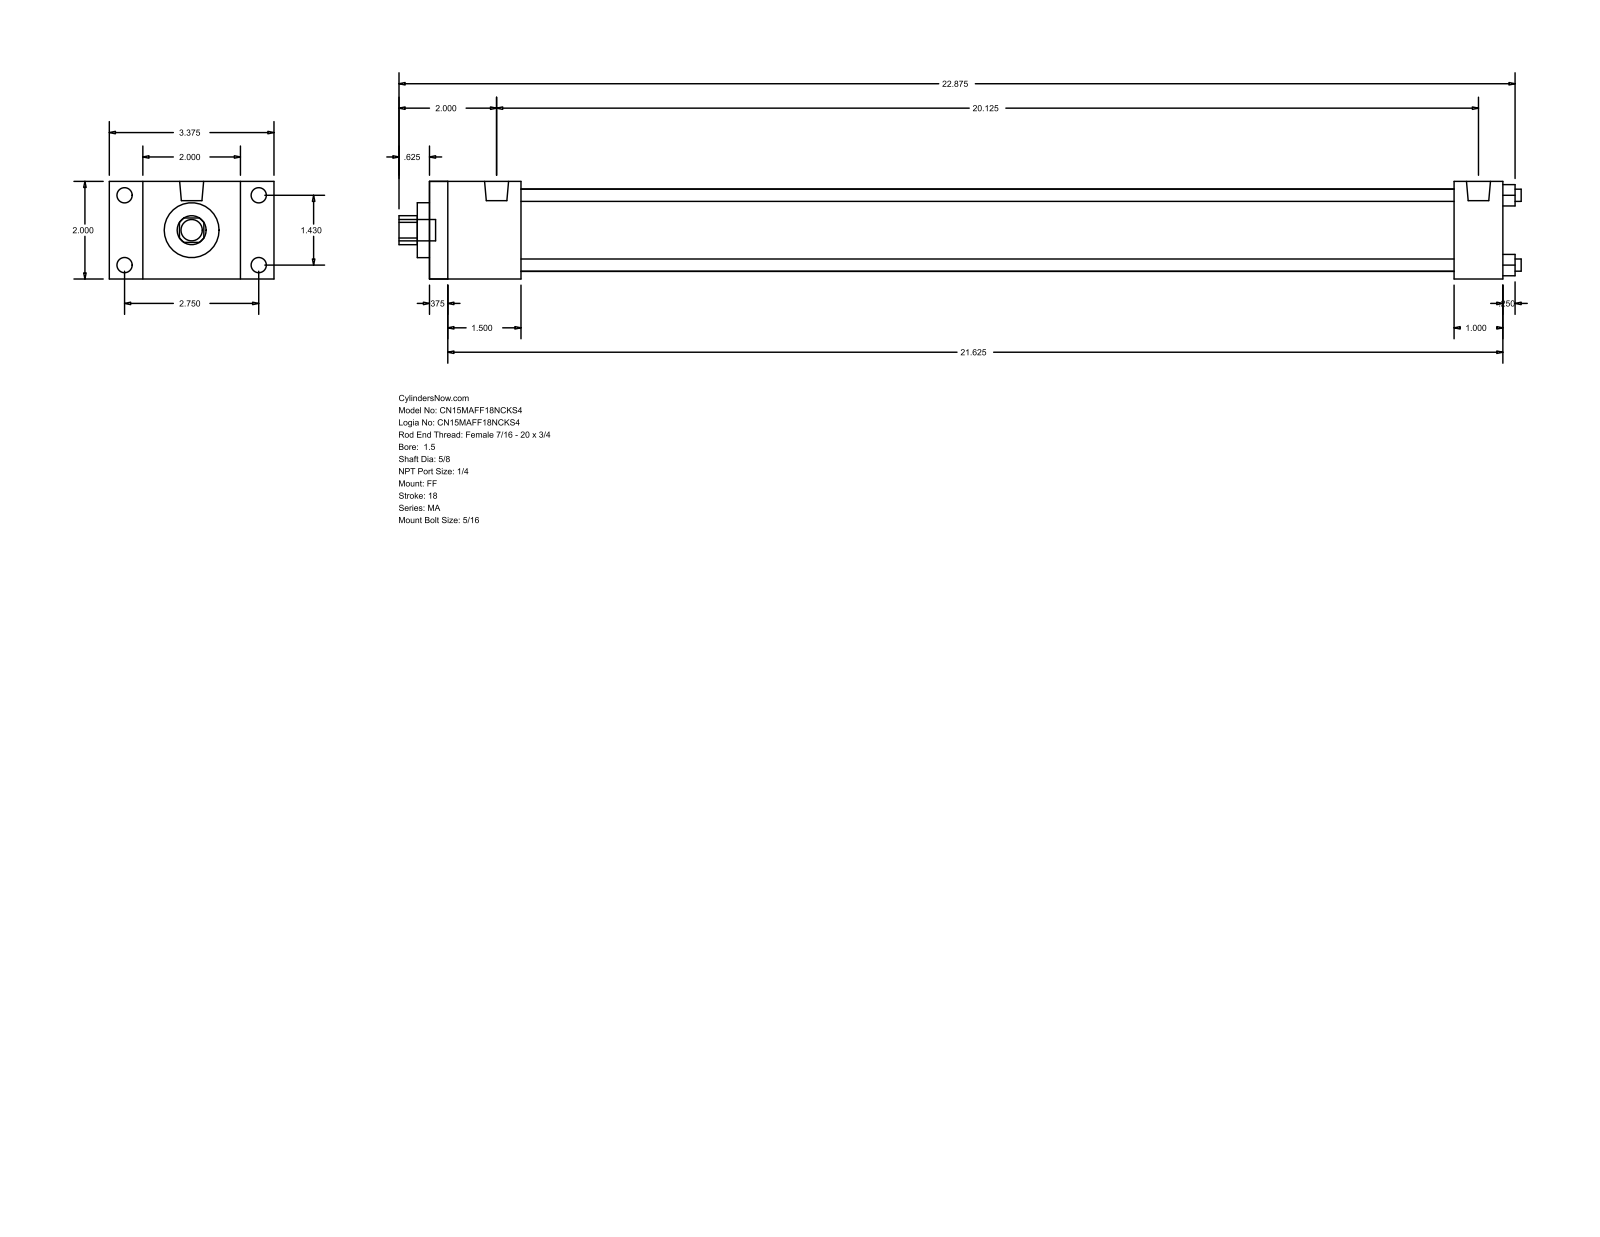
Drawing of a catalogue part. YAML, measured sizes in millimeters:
part_name: "MA_FF__0150_0.625"
step_written_by: "GSSL Pune (CONFIG_CONTROL_DESIGN)"
units: millimeters
bodies: {solids: 0, faces: 92, planar: 64, cylindrical: 28, other: 0}
overall_size: [584.2, 85.72, 50.8]
round_holes:
  - {diameter: 6.35, count: 4}
  - {diameter: 15.88, count: 1}
  - {diameter: 28.57, count: 1}
  - {diameter: 42.93, count: 1}
round_bosses_or_shafts:
  - {diameter: 7.94, count: 8}
  - {diameter: 12.49, count: 2}
  - {diameter: 11.11, count: 1}
partial_cylinders:
  - {radius: 7.54, count: 1}
face_to_face_distances: [50.8, 558.79, 9.52, 549.27, 25.4, 47.62, 533.39, 38.1, 523.87, 485.77]
hole_center_spacings: [25.68, 36.32, 51.36]
